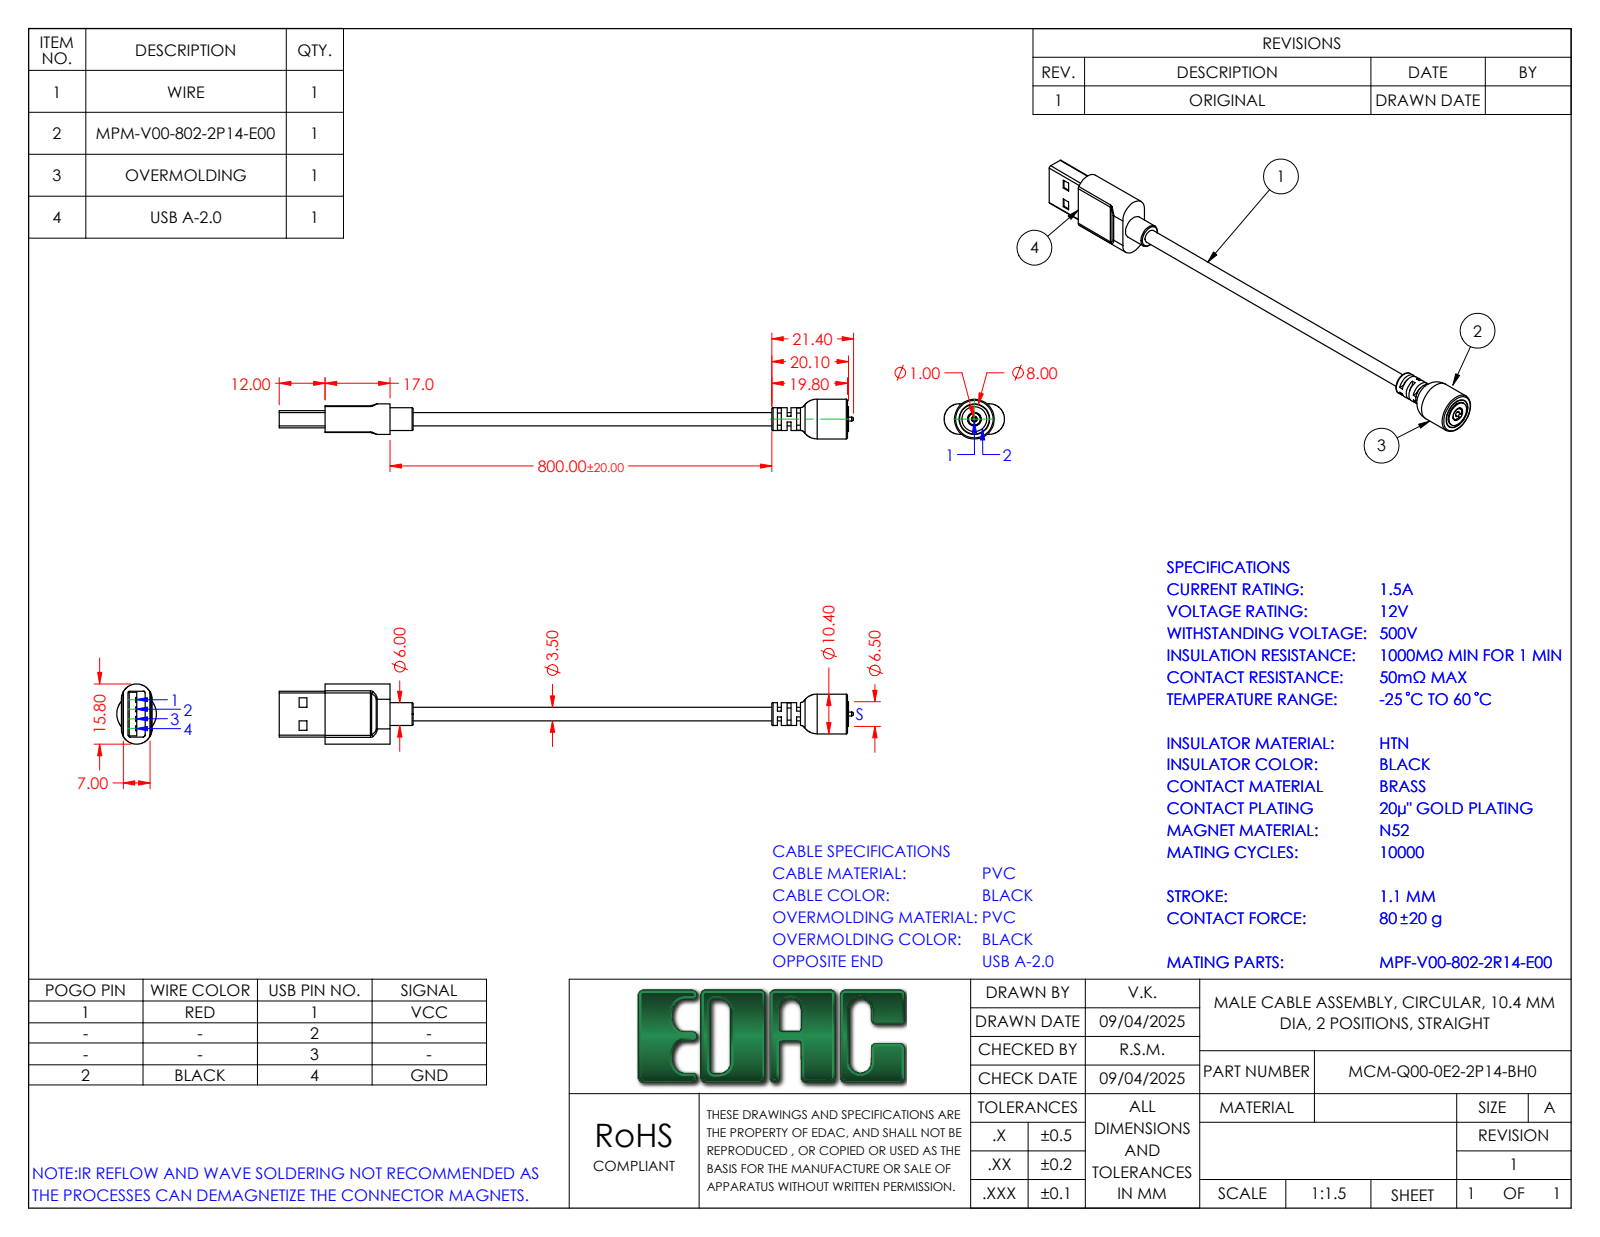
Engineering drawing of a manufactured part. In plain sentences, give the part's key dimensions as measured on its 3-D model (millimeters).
The part is named "MCM-Q00-0E2-2P14-BH0". Its 3-D file was written by "SolidWorks 2023 (CONFIG_CONTROL_DESIGN)". It is 0 solids with 169 faces: 85 planar, 52 cylindrical and 32 other. Overall it measures 150.4 by 15.8 by 10.4 millimeters. Round holes: 1 of diameter 0.8, 1 of diameter 1.5, 1 of diameter 2, 1 of diameter 3.6, 1 of diameter 8. Round bosses or shafts: 1 of diameter 10.4, 1 of diameter 6.5, 1 of diameter 6, 1 of diameter 3.5, 1 of diameter 1. Partial cylindrical surfaces (rounded edges, fillets, slot ends): 8 of radius 1, 6 of radius 0.1, 4 of radius 0.5, 2 of radius 4. The main face-to-face distances are 1.25, 5.75, 3.5, 4.2, 2.25, 5.45, 1.55, 7, 4.5, 1.75. The hole center spacings are 5.58.
